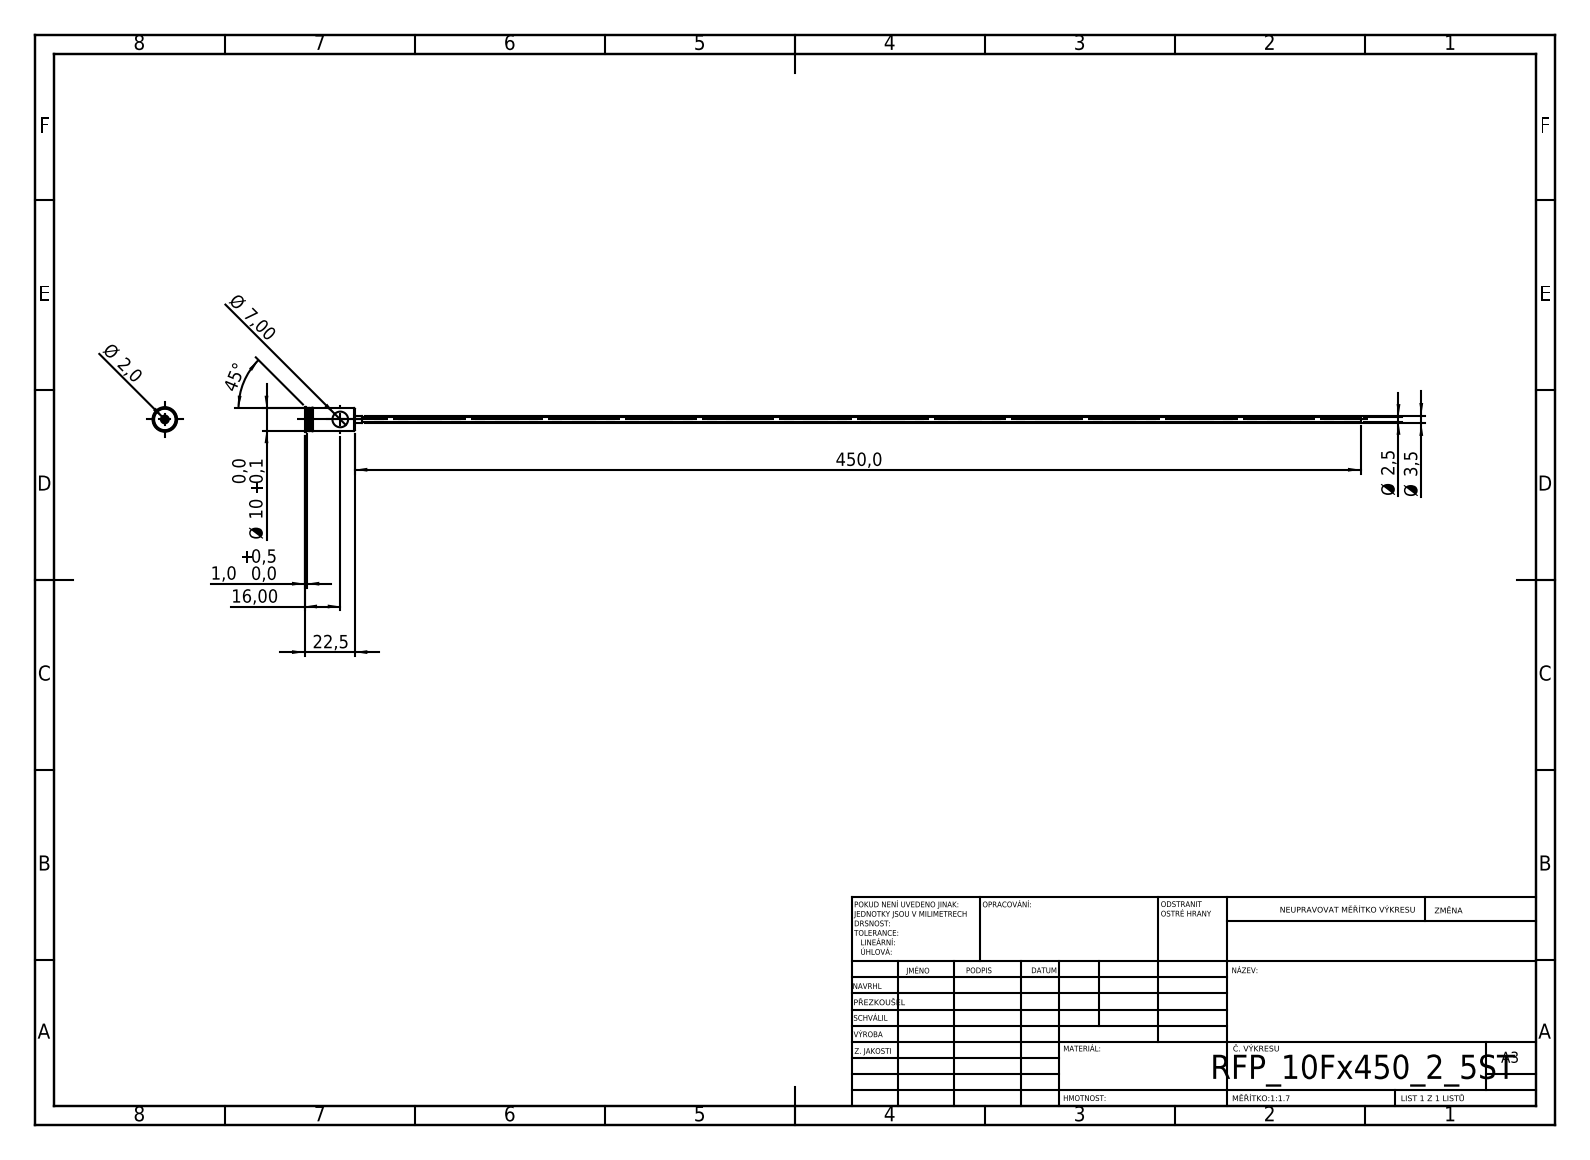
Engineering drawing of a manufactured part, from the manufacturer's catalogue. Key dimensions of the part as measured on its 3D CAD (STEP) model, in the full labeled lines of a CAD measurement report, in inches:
STEP written by: SolidWorks 2019 (CONFIG_CONTROL_DESIGN)
Units: inches
Bodies: 1 solid, 44 faces (20 planar, 16 cylindrical, 8 other)
Overall size (bounding box): 18.602 × 0.433 × 0.433
Volume: 0.132 in³ · Surface area: 11.53 in²
Round holes (diameter × count): ⌀0.079 ×1, ⌀0.276 ×1
Round bosses / shafts (diameter × count): ⌀0.433 ×1, ⌀0.394 ×1, ⌀0.138 ×1, ⌀0.098 ×1
Main face-to-face distances: 0.886, 0.807, 0.079, 0.213, 0.795, 0.091, 0.118, 0.913, 0.925, 1.004
